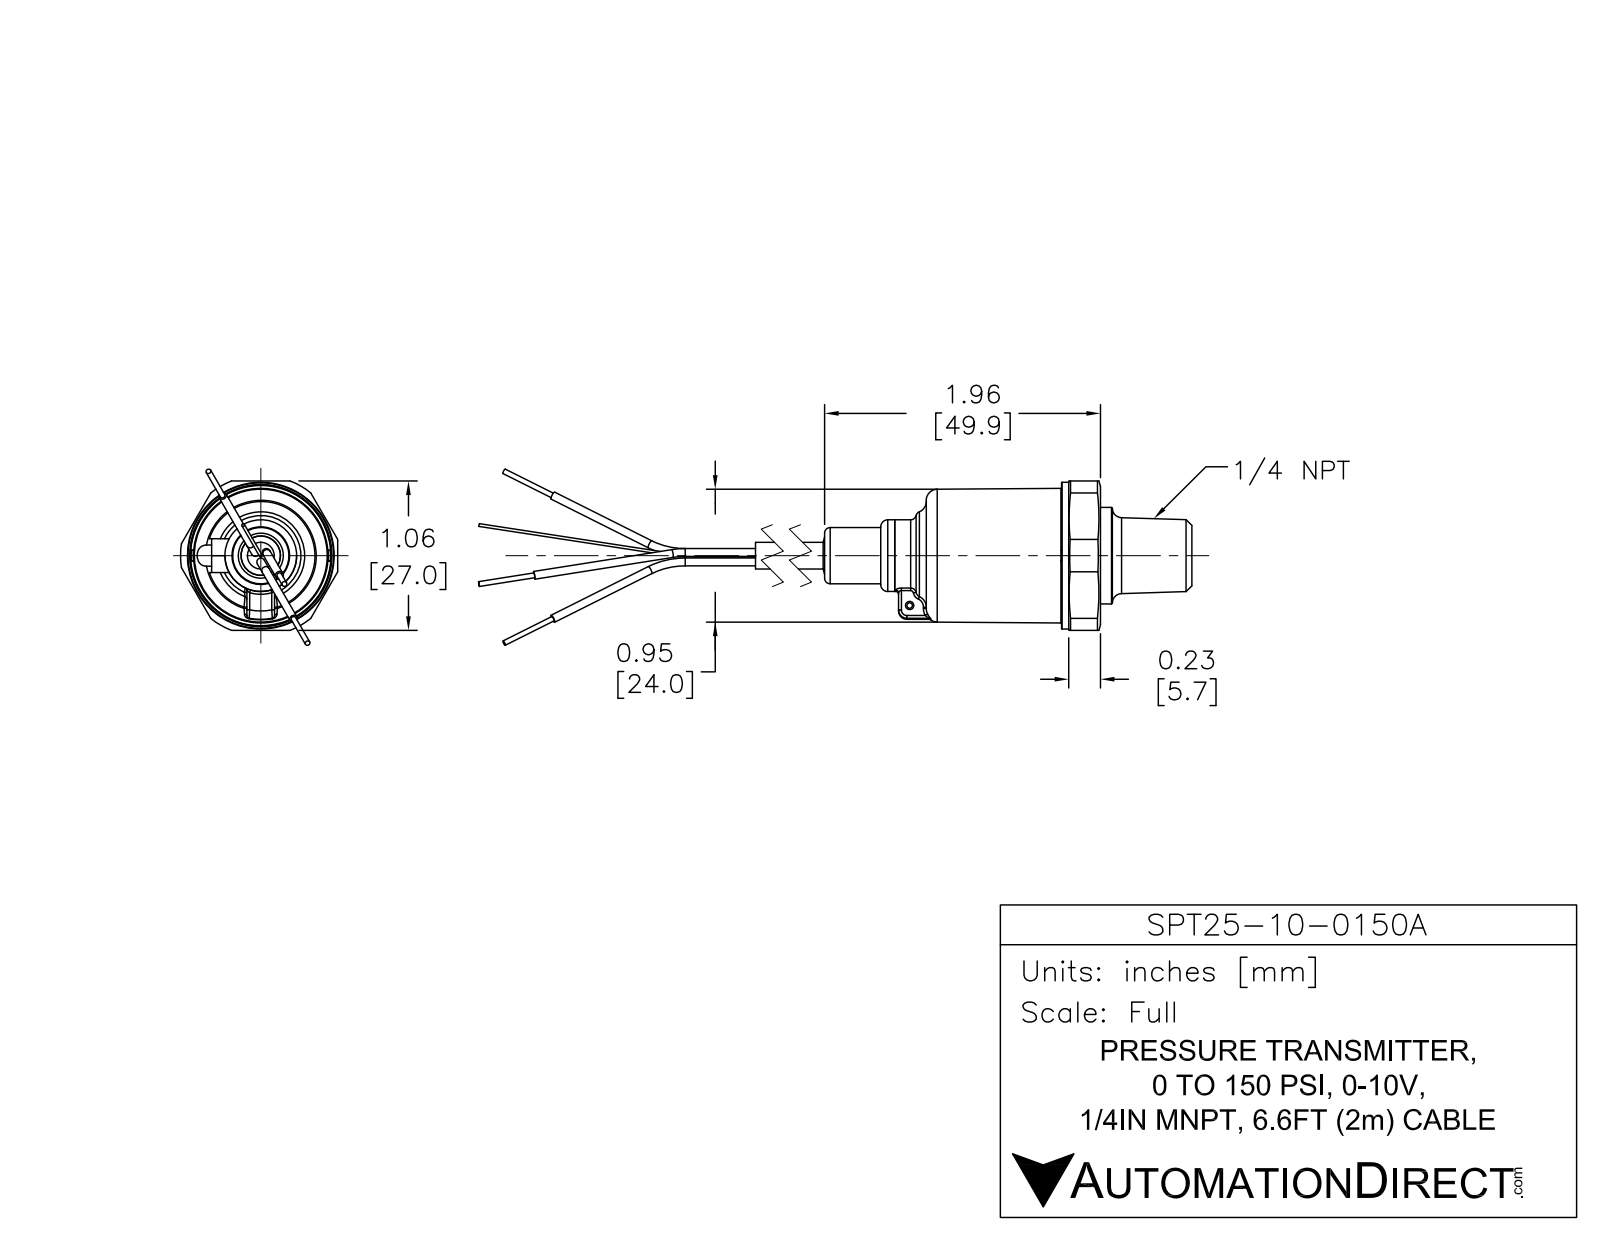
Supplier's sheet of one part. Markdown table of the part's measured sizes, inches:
| quantity | value |
| --- | --- |
| part name | SPT25-10-0150A |
| STEP written by | SolidWorks 2017 (AUTOMOTIVE_DESIGN) |
| units | inches |
| bodies | 7 solids, 116 faces (32 planar, 49 cylindrical, 35 other) |
| overall size | 6.035 × 1.142 × 1.067 |
| volume | 1.269 in³ |
| surface area | 11.11 in² |
| round holes (diameter × count) | 0.039 × 1, 0.13 × 1 |
| round bosses / shafts (diameter × count) | 0.055 × 6, 0.03 × 5, 1.053 × 1, 0.945 × 1, 0.689 × 1, 0.551 × 1, 0.512 × 1, 0.394 × 1 |
| partial cylindrical surfaces (radius × count) | 0.079 × 1, 0.571 × 1 |
| main face-to-face distances | 0.266, 0.945, 0.679, 1.683, 1.949, 2.628, 1.732, 0.049, 0.217, 0.896 |
